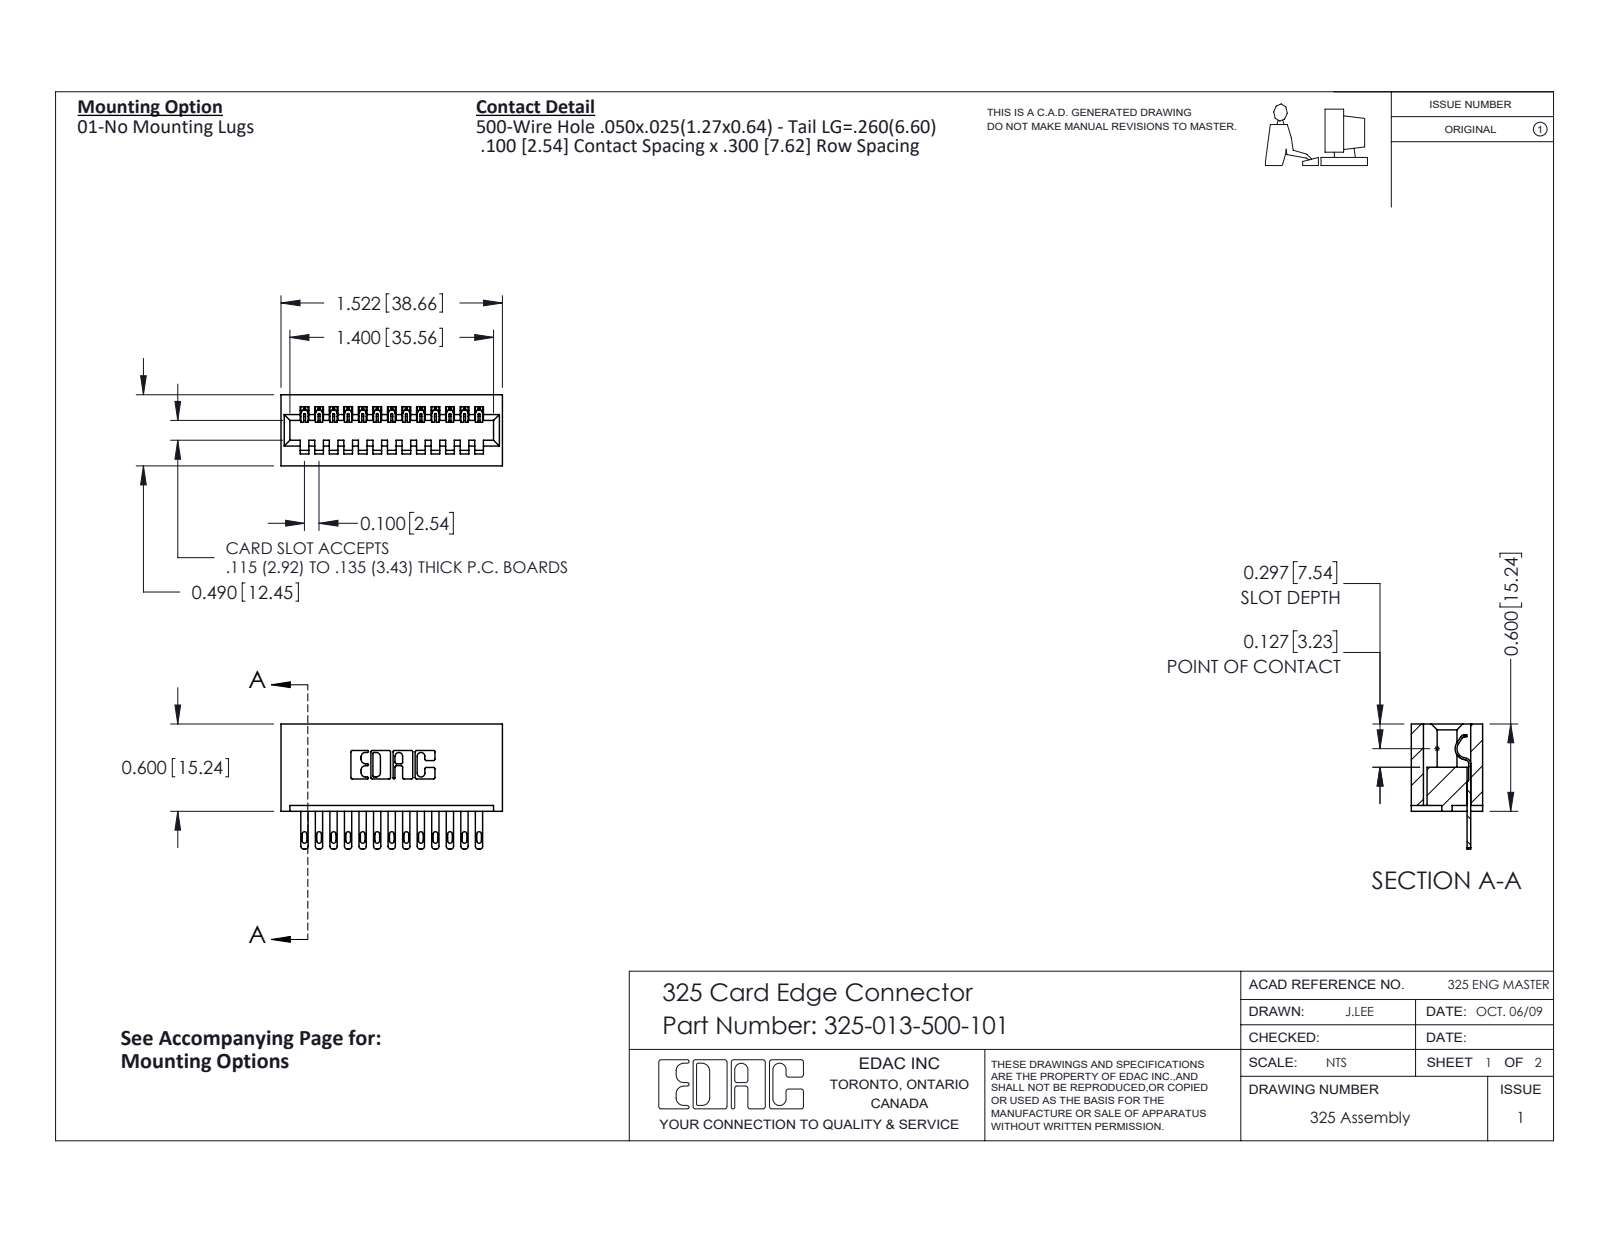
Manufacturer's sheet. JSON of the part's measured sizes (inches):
{"part_name": "325-013-500-101; 325-292-001_325-293-100; 325 Part_Lugless", "step_written_by": "SolidWorks 2016 (CONFIG_CONTROL_DESIGN)", "units": "inches", "bodies": {"solids": 14, "faces": 808, "planar": 534, "cylindrical": 274, "other": 0}, "overall_size": [1.522, 0.86, 0.49], "volume_in3": 0.321, "surface_area_in2": 8.951, "partial_cylinders_radius": [[0.006, 26], [0.016, 26], [0.02, 26], [0.01, 22], [0.007, 6], [0.031, 6], [0.026, 3], [0.014, 1]], "face_to_face_distances": [0.083, 0.407, 0.3, 0.1, 0.49, 0.2, 0.6, 0.4, 0.107, 0.383]}
